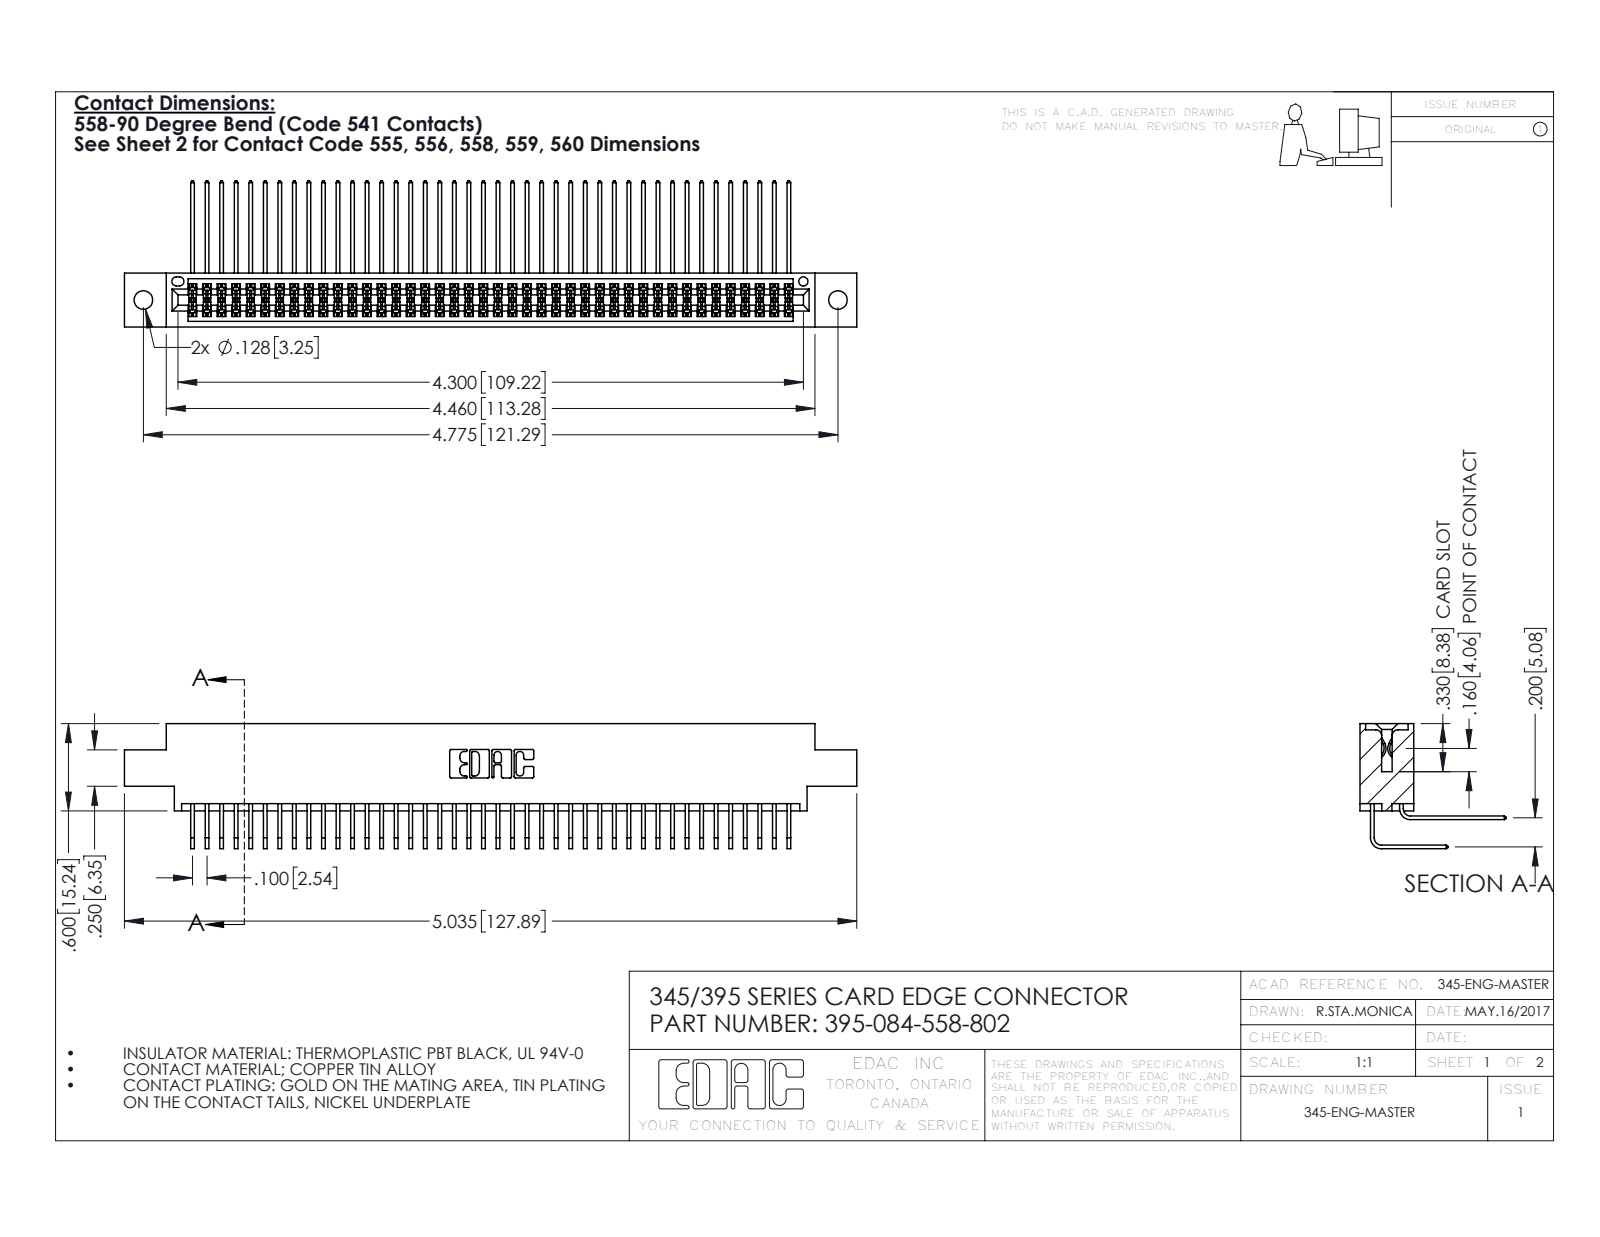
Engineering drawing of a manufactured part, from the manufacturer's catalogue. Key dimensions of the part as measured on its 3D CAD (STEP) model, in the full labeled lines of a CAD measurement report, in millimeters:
Part name (STEP PRODUCT): 395-084-558-802; 345 Part_0.170 Offset - 0.128 Dia; 345-292-001_558 Tail - 2; 345-292-001_558 559 Tail - 1
STEP written by: SolidWorks 2016 (CONFIG_CONTROL_DESIGN)
Units: millimetres
Bodies: 85 solids, 4498 faces (3024 planar, 1474 cylindrical, 0 other)
Overall size (bounding box): 127.9 × 25.5 × 21.8
Volume: 12 800 mm³ · Surface area: 21 010 mm²
Round holes (diameter × count): ⌀3.3 ×2, ⌀1.6 ×1
Partial cylindrical surfaces — rounded edges, fillets, slot ends (radius × count): R0.2 ×127, R0.3 ×22, R0.2 ×6, R0.8 ×6, R0.7 ×3, R0.4 ×2, R0.5 ×2, R0.6 ×2
Main face-to-face distances: 1.8, 7.6, 5.1, 9.4, 2.5, 6.9, 0.6, 5.7, 4.4, 0.6
Hole centre spacings: 6.9, 115.3, 121.3
